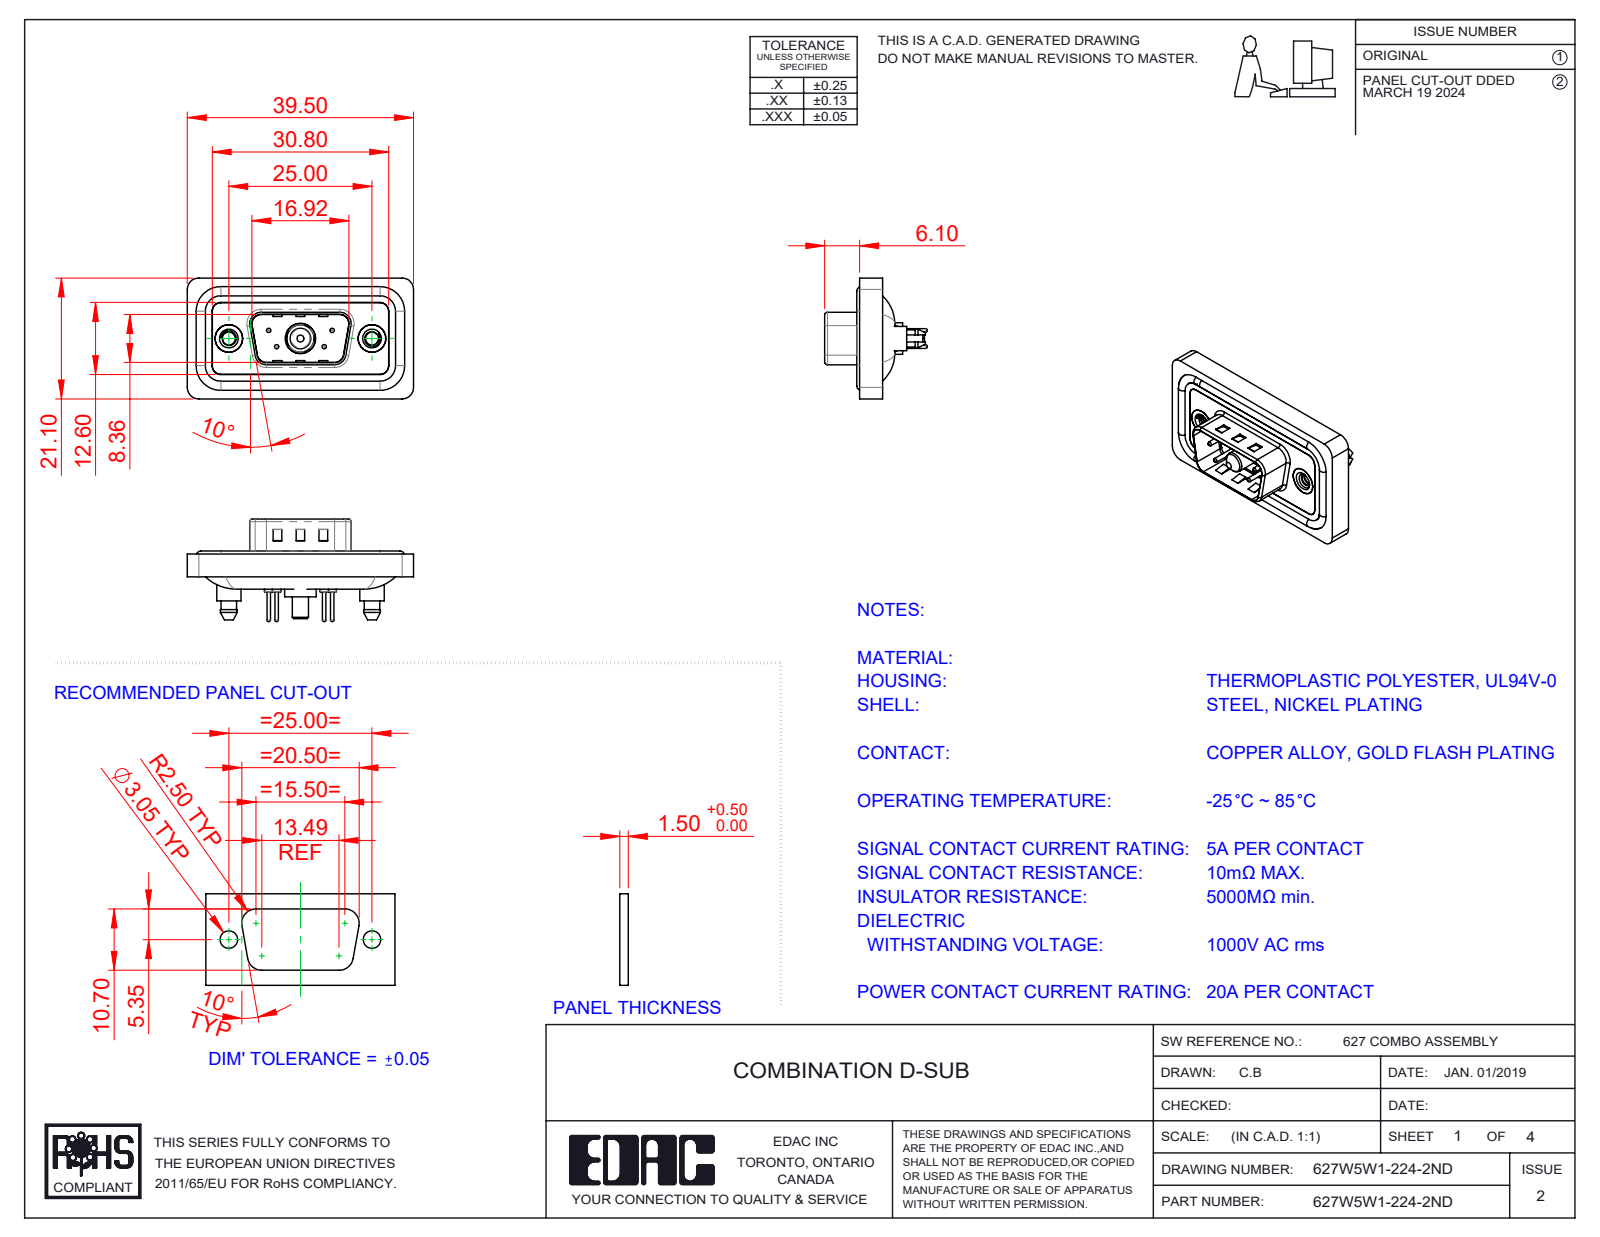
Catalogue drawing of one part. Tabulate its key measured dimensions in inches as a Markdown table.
| quantity | value |
| --- | --- |
| part name | 627Combo Shell Rear_09 Contacts; Power Pin_20A S; 627Combo Contact Row 1_24; 627Combo Housing_5W1 (+6 more) |
| STEP written by | SolidWorks 2023 (CONFIG_CONTROL_DESIGN) |
| units | inches |
| bodies | 13 solids, 656 faces (199 planar, 295 cylindrical, 162 other) |
| overall size | 1.555 × 0.831 × 0.705 |
| volume | 0.276 in³ |
| surface area | 11.28 in² |
| round holes (diameter × count) | 0.03 × 4, 0.063 × 4, 0.079 × 4, 0.089 × 2, 0.157 × 2, 0.189 × 2, 0.197 × 2, 0.191 × 1, 0.209 × 1 |
| round bosses / shafts (diameter × count) | 0.063 × 4, 0.059 × 4, 0.024 × 4, 0.213 × 2, 0.193 × 2, 0.167 × 2, 0.217 × 1, 0.205 × 1 |
| partial cylindrical surfaces (radius × count) | 0.059 × 24, 0.079 × 18, 0.063 × 10, 0.02 × 8, 0.01 × 4, 0.024 × 4, 0.026 × 4, 0.035 × 4 |
| main face-to-face distances | 0.016, 0.043, 0.114, 0.063, 0.059, 0.122, 0.02, 0.098, 0.157, 0.031 |
| hole center spacings | 0.124, 0.225, 0.28, 0.492, 0.713, 0.173, 0.173, 0.327 |
